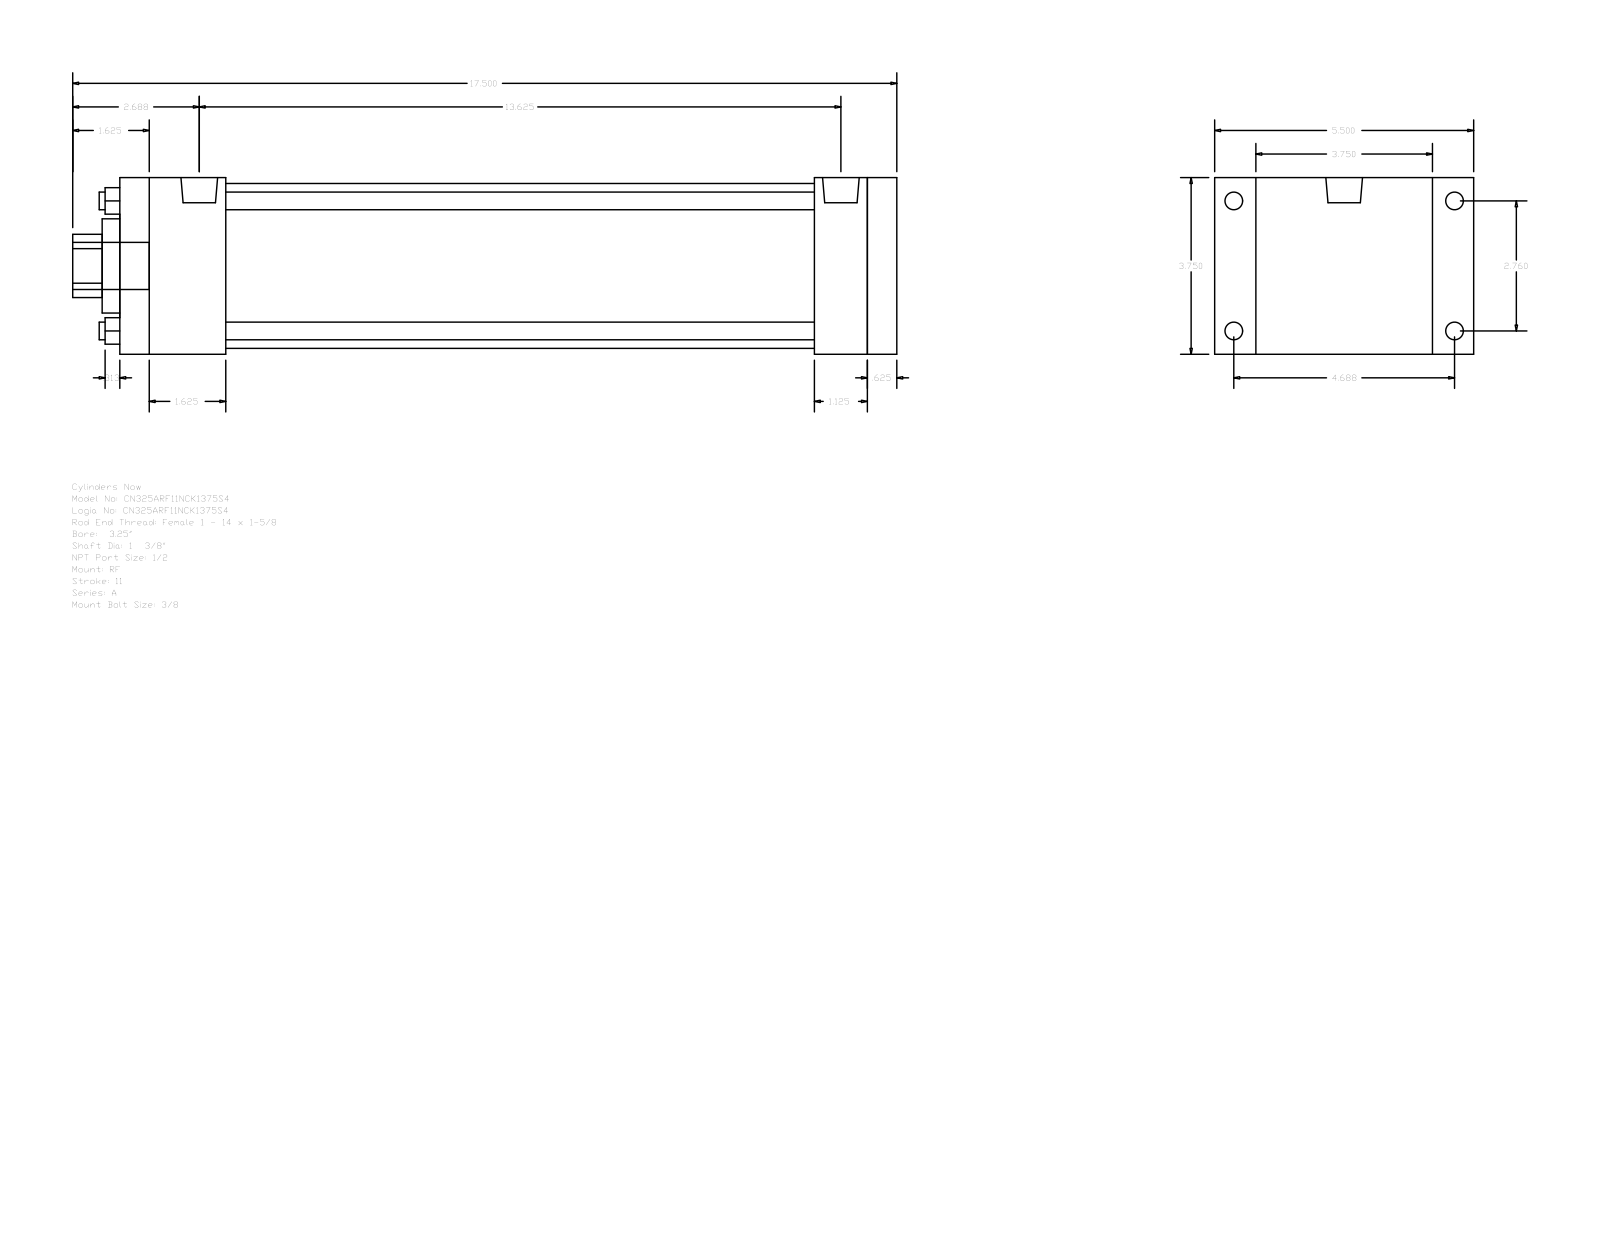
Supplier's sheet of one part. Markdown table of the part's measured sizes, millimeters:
| quantity | value |
| --- | --- |
| part name | A_RF__0325_1.375 |
| STEP written by | GSSL Pune (CONFIG_CONTROL_DESIGN) |
| units | millimeters |
| bodies | 0 solids, 92 faces (64 planar, 28 cylindrical, 0 other) |
| overall size | 444.5 × 139.7 × 95.25 |
| round holes (diameter × count) | 9.53 × 4, 34.92 × 1, 50.8 × 1, 88.9 × 1 |
| round bosses / shafts (diameter × count) | 9.53 × 4, 8.73 × 4, 19.77 × 2, 25.4 × 1 |
| partial cylindrical surfaces (radius × count) | 17.06 × 1 |
| main face-to-face distances | 95.24, 419.1, 15.88, 403.22, 22.23, 117.47, 28.57, 374.65, 44.45, 57.15 |
| hole center spacings | 49.57, 70.1, 99.14 |
